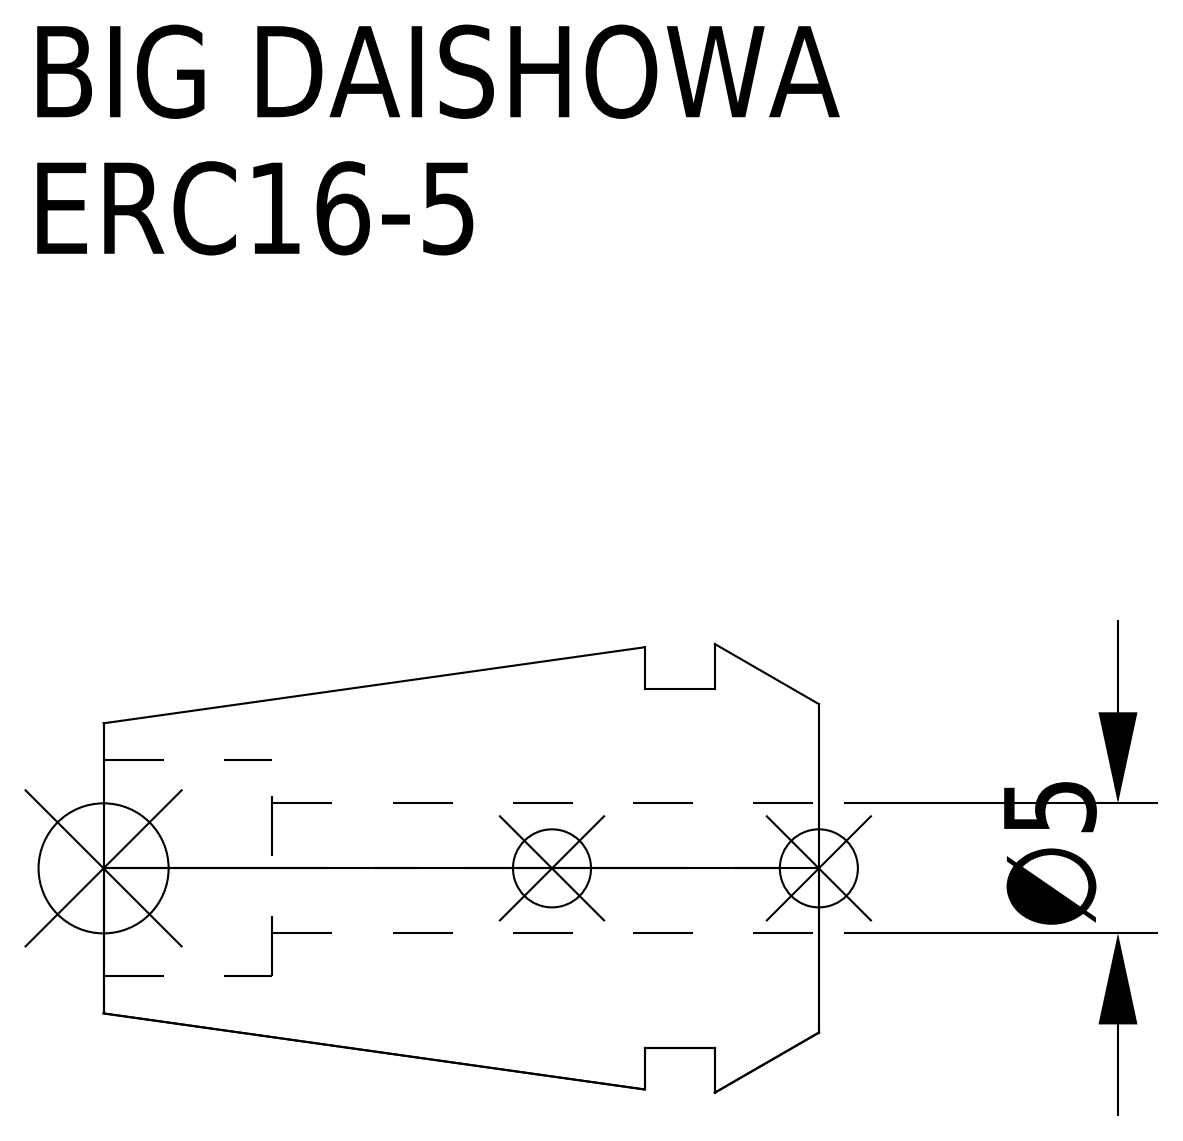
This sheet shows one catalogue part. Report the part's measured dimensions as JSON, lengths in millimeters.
{"part_name": "ERC16-5", "step_written_by": "CREO PARAMETRIC BY PTC INC, 2016380 (AUTOMOTIVE_DESIGN)", "units": "millimeters", "bodies": {"solids": 1, "faces": 15, "planar": 5, "cylindrical": 6, "other": 4}, "overall_size": [27.5, 17.25, 17.25], "volume_mm3": 3631, "surface_area_mm2": 2107, "round_holes": [[5, 1], [8.3, 1]], "round_bosses_or_shafts": [[13.8, 1]], "face_to_face_distances": [4, 6.7, 2.7, 27.5, 23.5, 20.8, 21.01, 17.01, 14.31, 6.49]}
